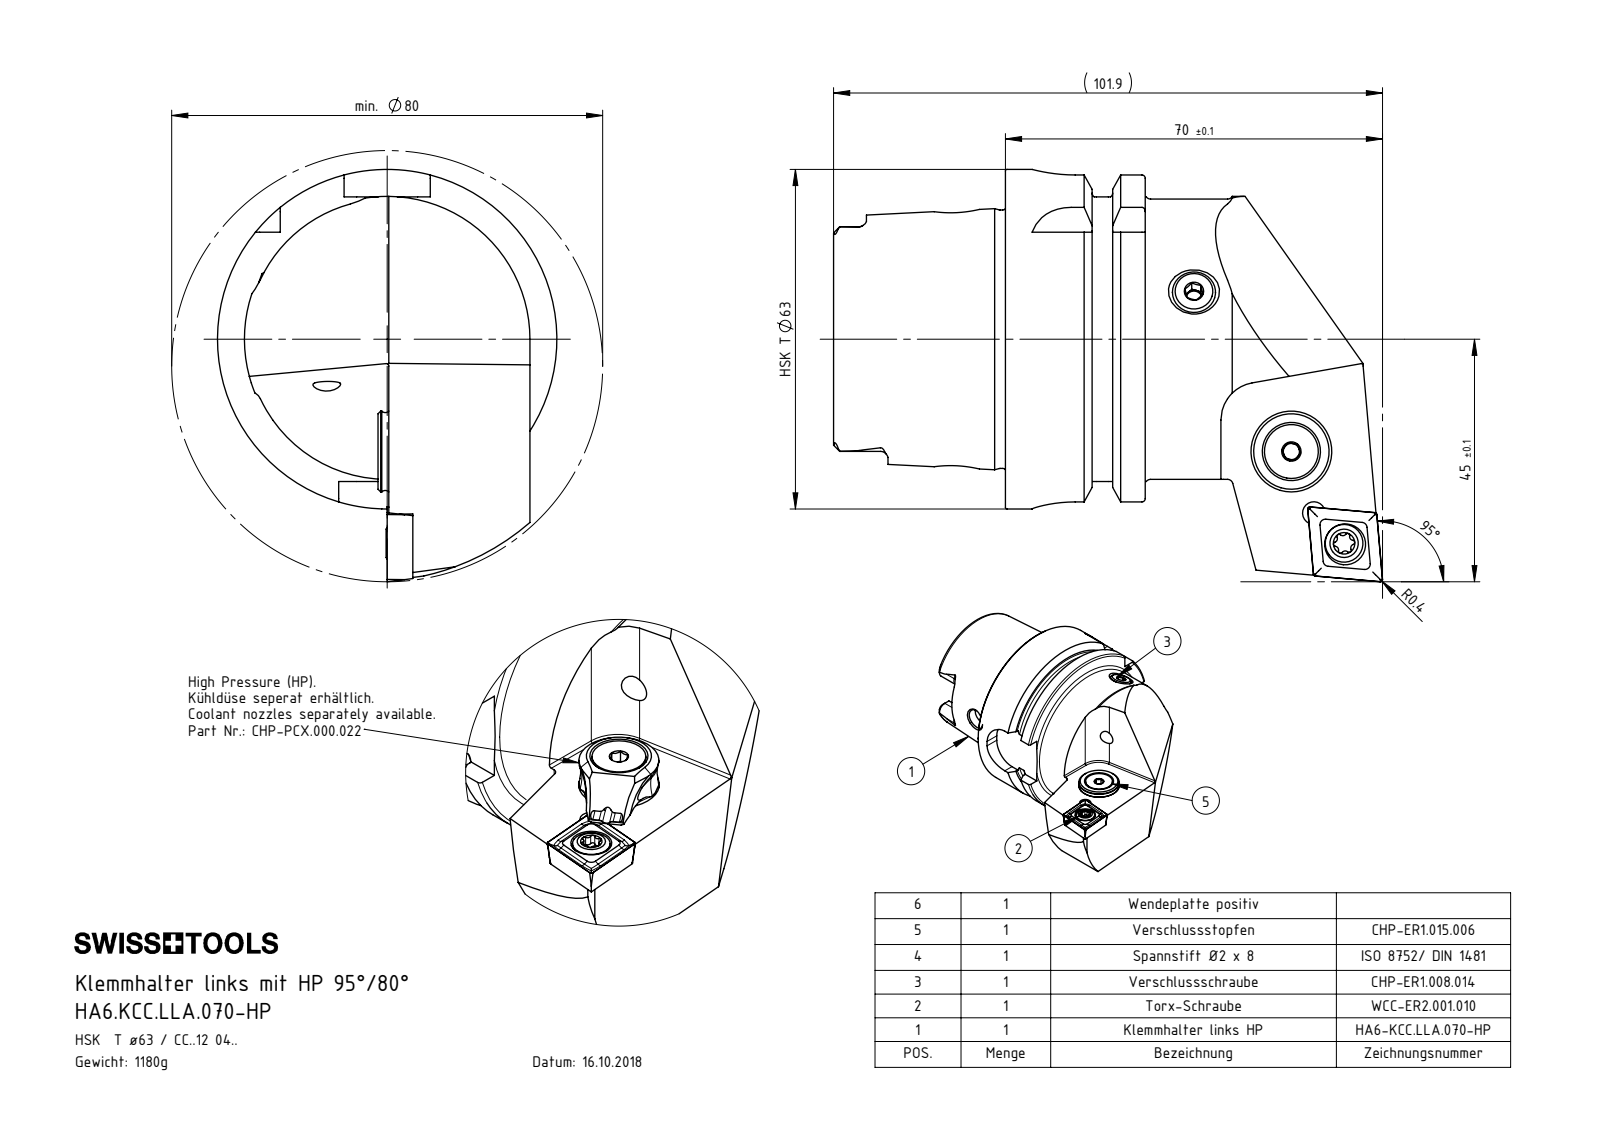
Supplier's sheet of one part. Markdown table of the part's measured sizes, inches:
| quantity | value |
| --- | --- |
| part name | WCC-ER2.001.010_A; CHP-ER1.015.006; HA6-KCC.LLA.070-HP_A; CHP-ER1.008.014_A (+6 more) |
| STEP written by | SolidWorks 2017 (AUTOMOTIVE_DESIGN) |
| units | inches |
| bodies | 8 solids, 301 faces (116 planar, 75 cylindrical, 110 other) |
| overall size | 4.012 × 3.012 × 2.48 |
| volume | 9.194 in³ |
| surface area | 52.53 in² |
| round holes (diameter × count) | 0.165 × 4, 0.197 × 2, 0.047 × 1, 0.079 × 1, 0.098 × 1, 0.118 × 1, 0.205 × 1, 0.217 × 1, 0.276 × 1, 0.295 × 1, 0.299 × 1, 0.331 × 1 |
| round bosses / shafts (diameter × count) | 0.197 × 2, 2.48 × 1, 2.163 × 1, 2.047 × 1, 1.887 × 1, 0.591 × 1, 0.528 × 1, 0.394 × 1 |
| partial cylindrical surfaces (radius × count) | 0.015 × 6, 0.055 × 6, 0.315 × 4, 0.027 × 3, 0.027 × 3, 0.02 × 2, 0.111 × 2, 0.113 × 2 |
| main face-to-face distances | 1.031, 1.022, 0.63, 0.392, 1.256, 1.648, 2.278, 2.079, 0.858, 0.467 |
| hole center spacings | 0.177, 0.312, 0.323, 0.4, 0.478, 0.657, 0.667, 0.773 |
